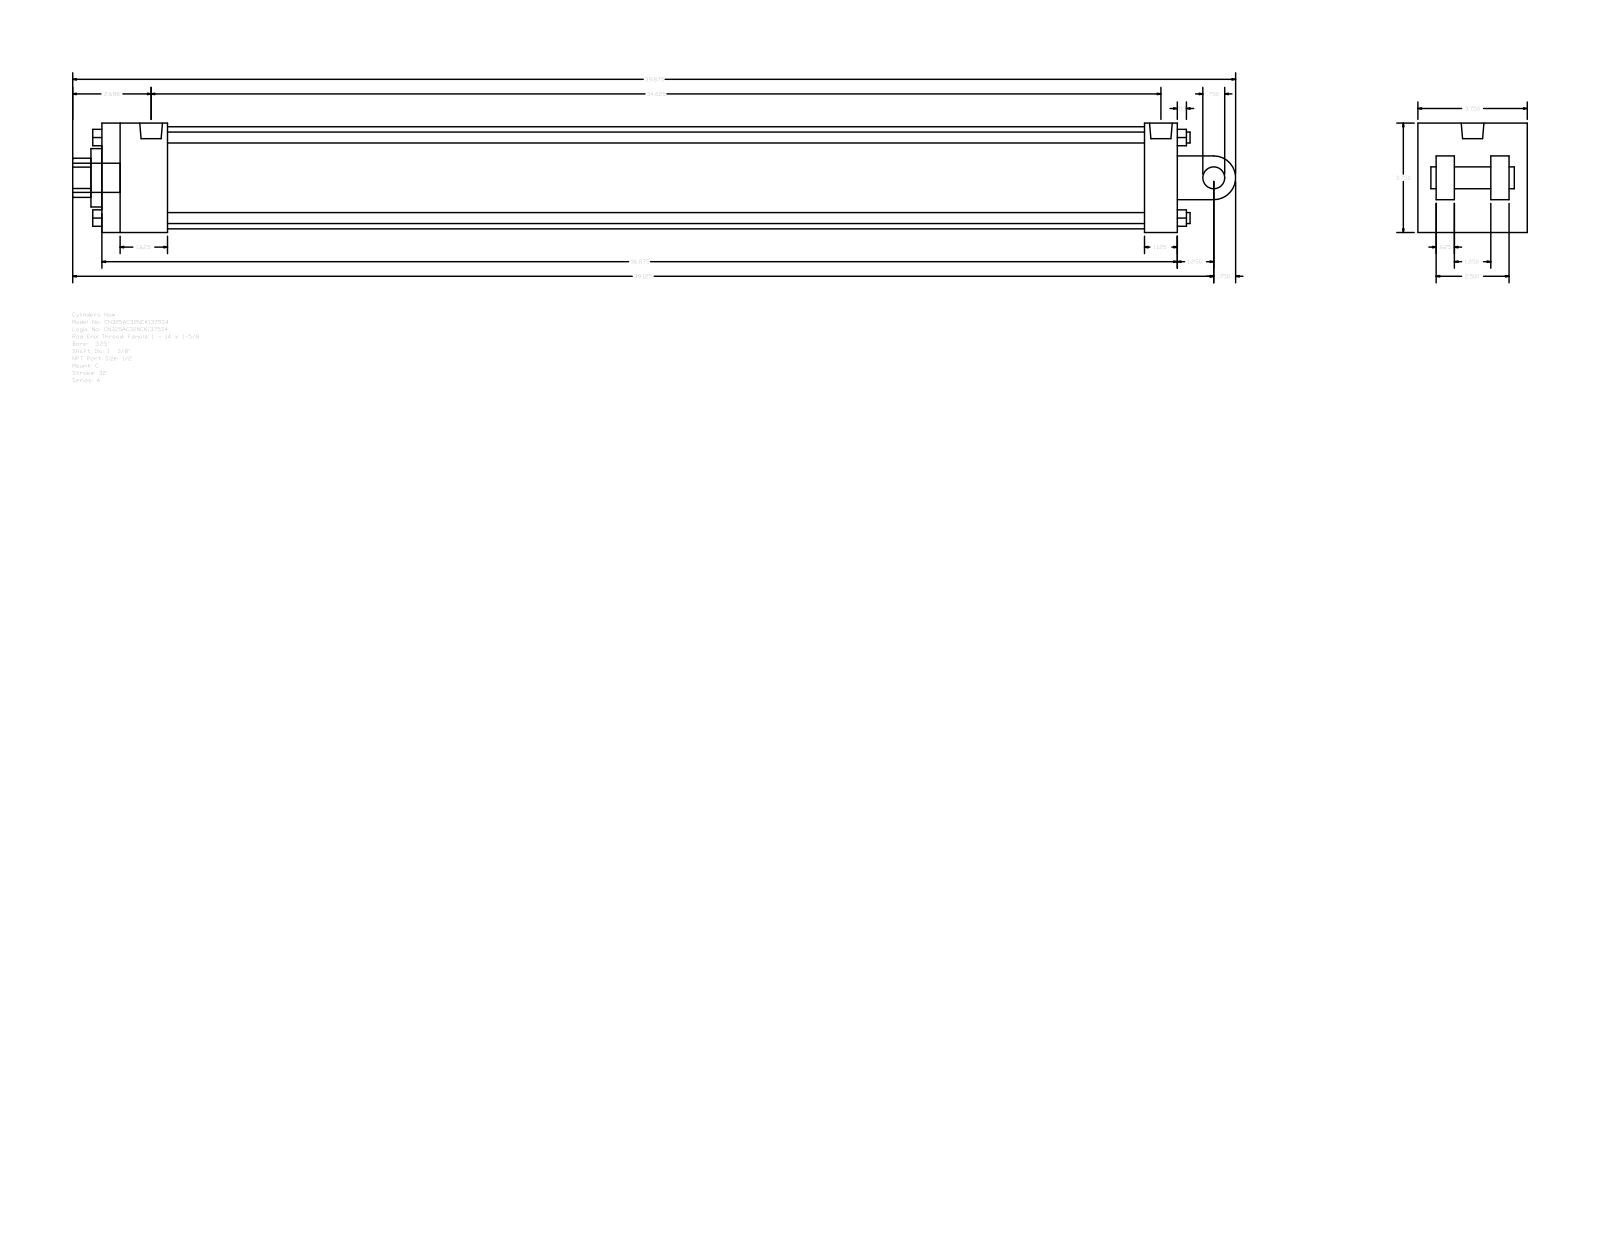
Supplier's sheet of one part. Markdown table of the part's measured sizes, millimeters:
| quantity | value |
| --- | --- |
| part name | A_C__0325_1.375 |
| STEP written by | GSSL Pune (CONFIG_CONTROL_DESIGN) |
| units | millimeters |
| bodies | 0 solids, 135 faces (102 planar, 33 cylindrical, 0 other) |
| overall size | 1012.83 × 95.25 × 95.25 |
| round holes (diameter × count) | 8.73 × 2, 19.77 × 1, 34.92 × 1, 50.8 × 1, 88.9 × 1 |
| round bosses / shafts (diameter × count) | 9.53 × 4, 8.73 × 2, 25.4 × 1, 19.77 × 1, 19.05 × 1 |
| partial cylindrical surfaces (radius × count) | 17.06 × 1, 19.05 × 1 |
| main face-to-face distances | 95.24, 15.87, 936.62, 28.57, 63.5, 66.67, 31.74, 79.37, 47.63, 908.05 |
| hole center spacings | 3.18 |
